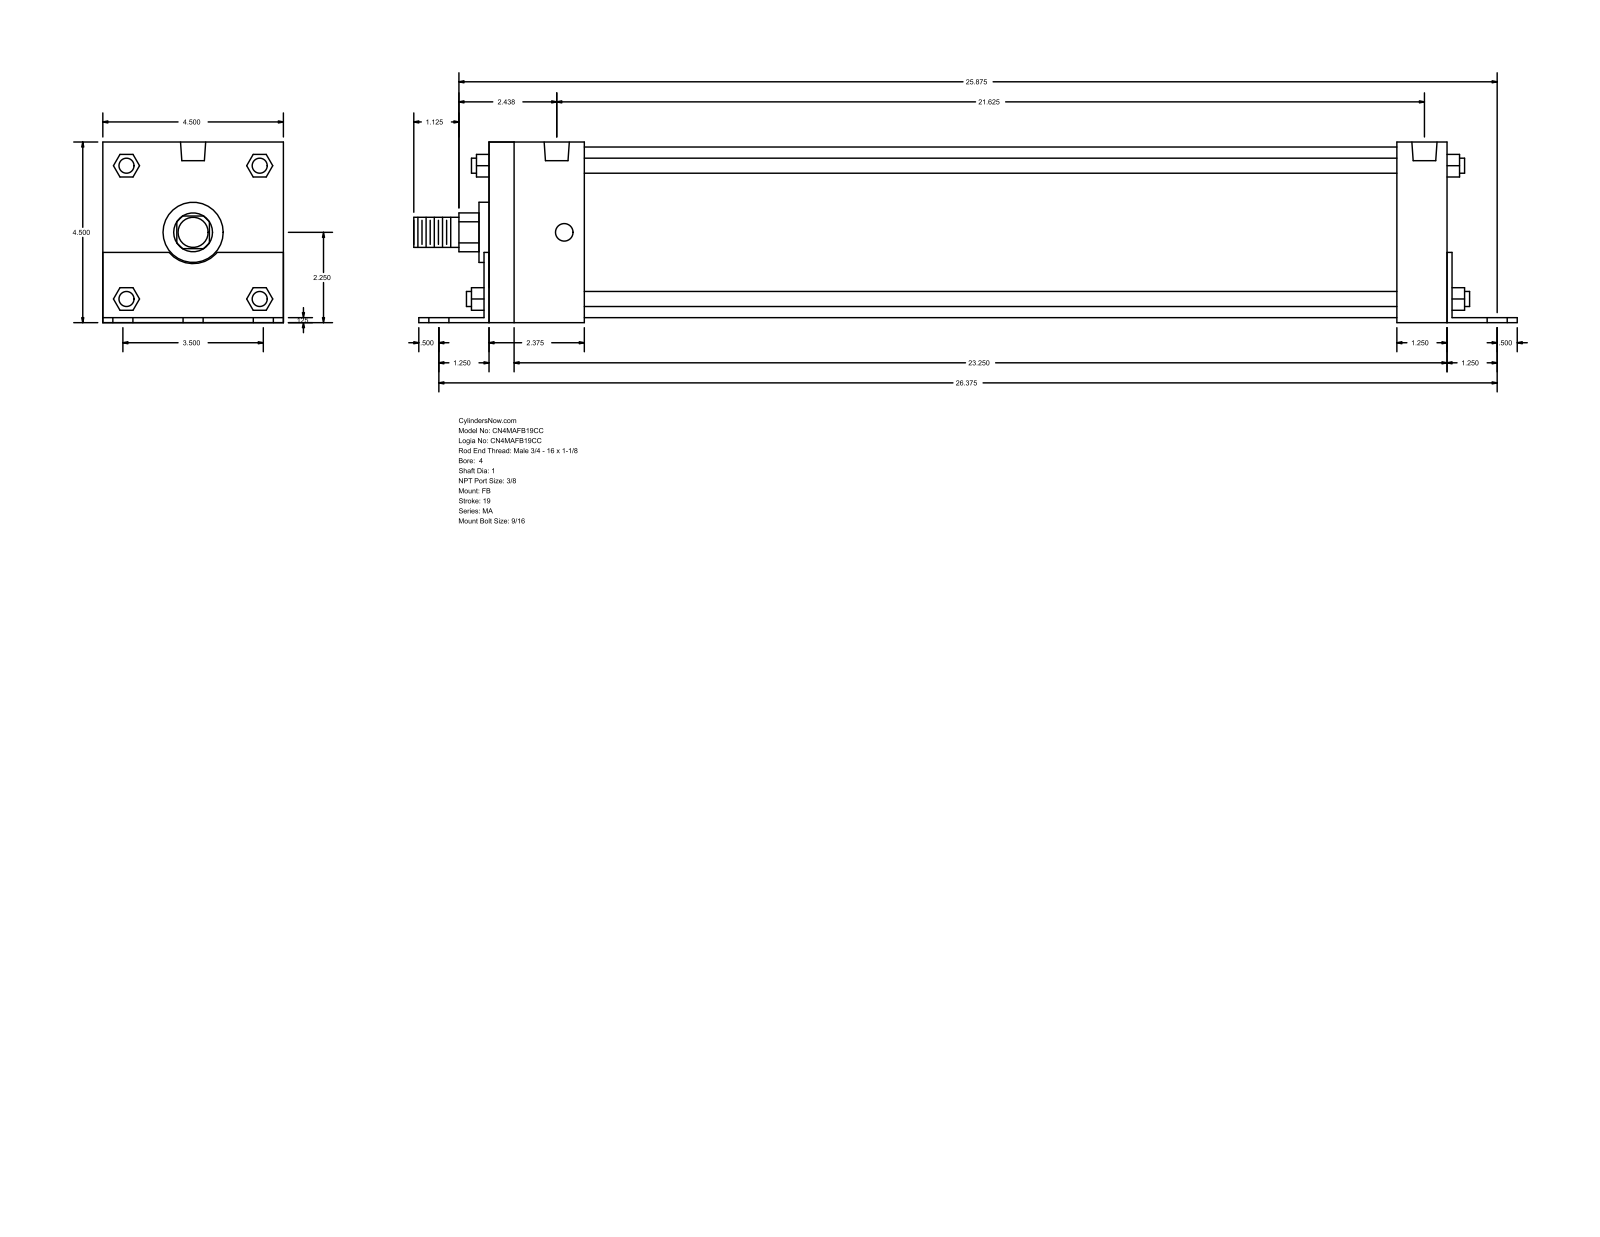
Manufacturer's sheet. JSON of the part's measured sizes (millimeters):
{"part_name": "MA_FB__0400_1", "step_written_by": "GSSL Pune (CONFIG_CONTROL_DESIGN)", "units": "millimeters", "bodies": {"solids": 0, "faces": 140, "planar": 105, "cylindrical": 35, "other": 0}, "overall_size": [698.5, 114.35, 114.3], "round_holes": [[14.29, 6], [11.11, 4], [15.93, 2]], "round_bosses_or_shafts": [[9.53, 4], [107.95, 1], [38.1, 1], [25.4, 1], [19.05, 1]], "partial_cylinders_radius": [[12.29, 1], [19.81, 1]], "face_to_face_distances": [114.3, 3.17, 114.35, 609.6, 3.12, 111.18, 606.43, 612.77, 577.85, 574.68], "hole_center_spacings": [44.45, 671.4, 669.93, 64, 67.51, 86.85, 88.9, 90.97]}
